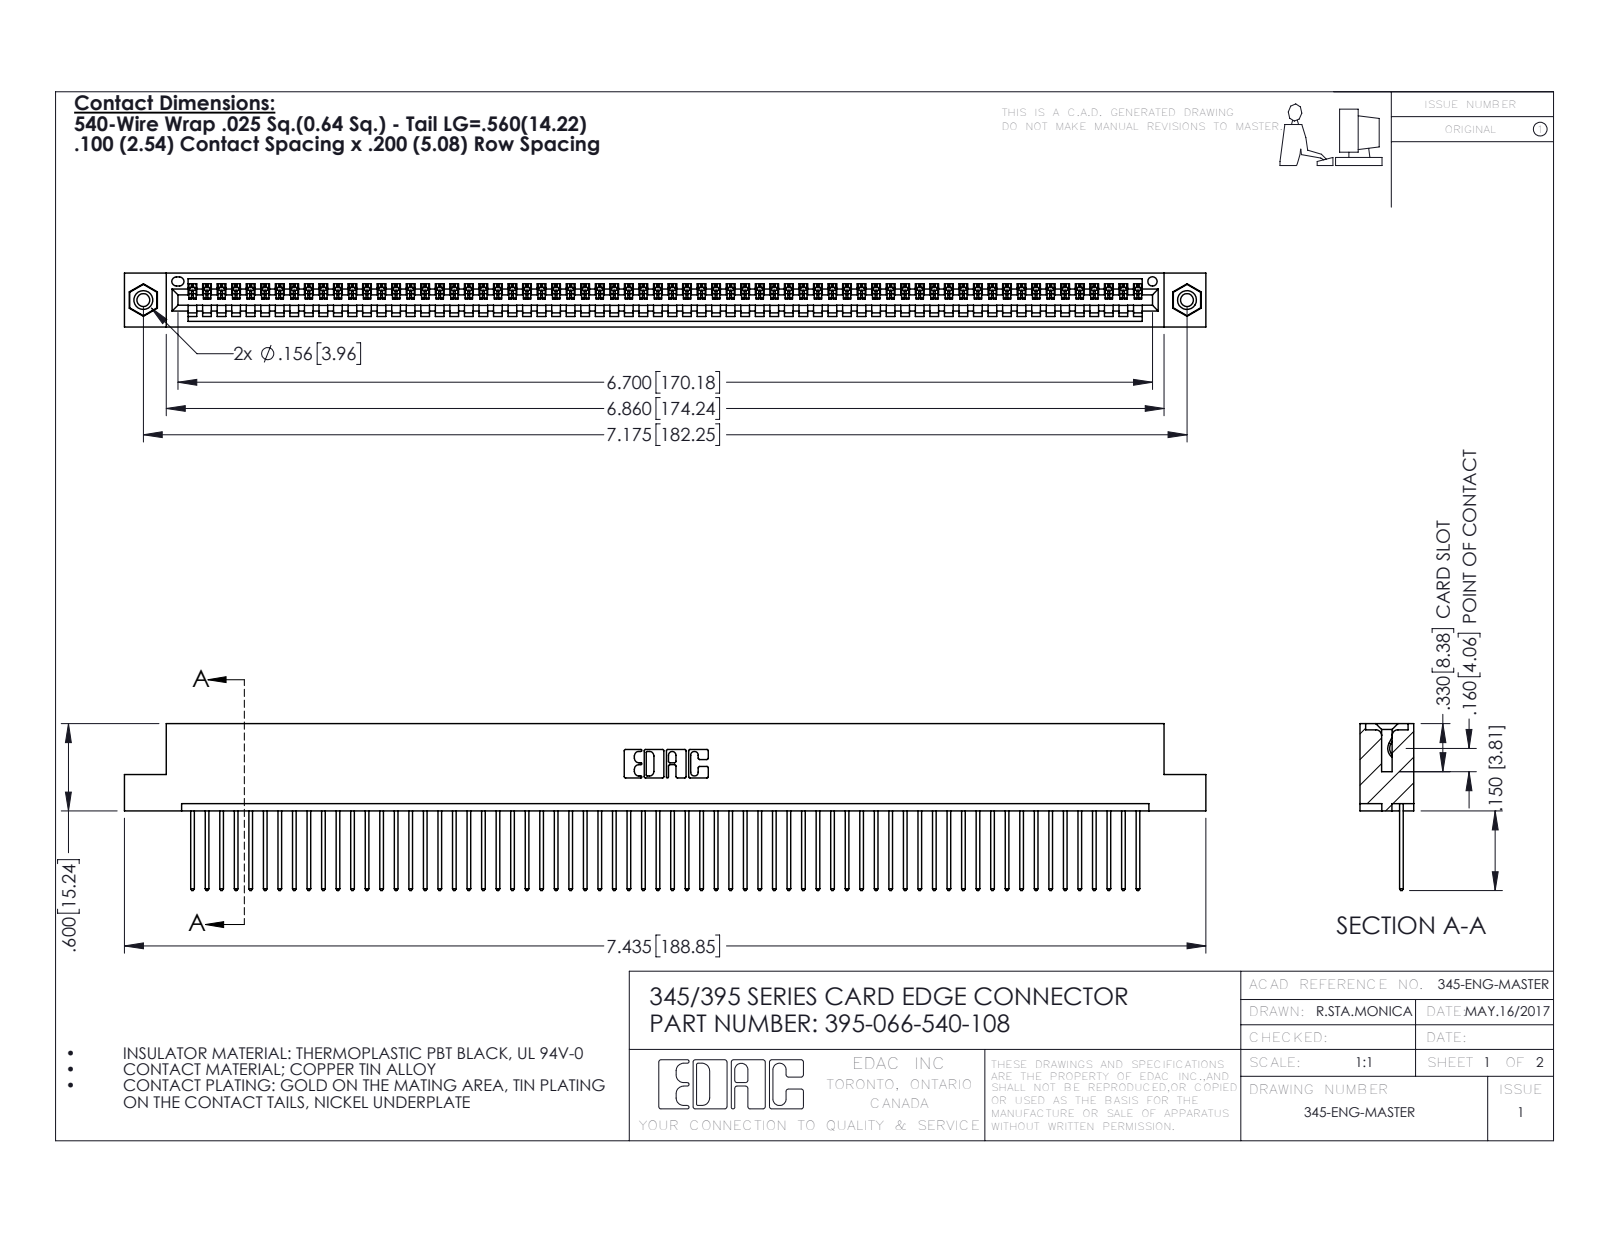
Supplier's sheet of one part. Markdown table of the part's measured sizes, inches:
| quantity | value |
| --- | --- |
| part name | 395-066-540-108; 345-250-001_345-250-003-102; 345-292-001_345-293-140; 345 Part_Flush Mounting Lugs - 0.156 Dia-TI |
| STEP written by | SolidWorks 2016 (CONFIG_CONTROL_DESIGN) |
| units | inches |
| bodies | 69 solids, 4014 faces (2752 planar, 1246 cylindrical, 16 other) |
| overall size | 7.435 × 1.147 × 0.37 |
| volume | 1.112 in³ |
| surface area | 39.05 in² |
| round holes (diameter × count) | 0.089 × 2, 0.125 × 2, 0.156 × 2, 0.064 × 1 |
| round bosses / shafts (diameter × count) | 0.155 × 2 |
| partial cylindrical surfaces (radius × count) | 0.006 × 132, 0.01 × 132, 0.01 × 22, 0.007 × 6, 0.031 × 6, 0.026 × 3, 0.031 × 2, 0.04 × 2 |
| main face-to-face distances | 0.072, 0.298, 0.37, 0.098, 0.272, 0.025, 0.2, 0.225, 0.149, 0.072 |
| hole center spacings | 0.27, 6.939, 7.175 |
